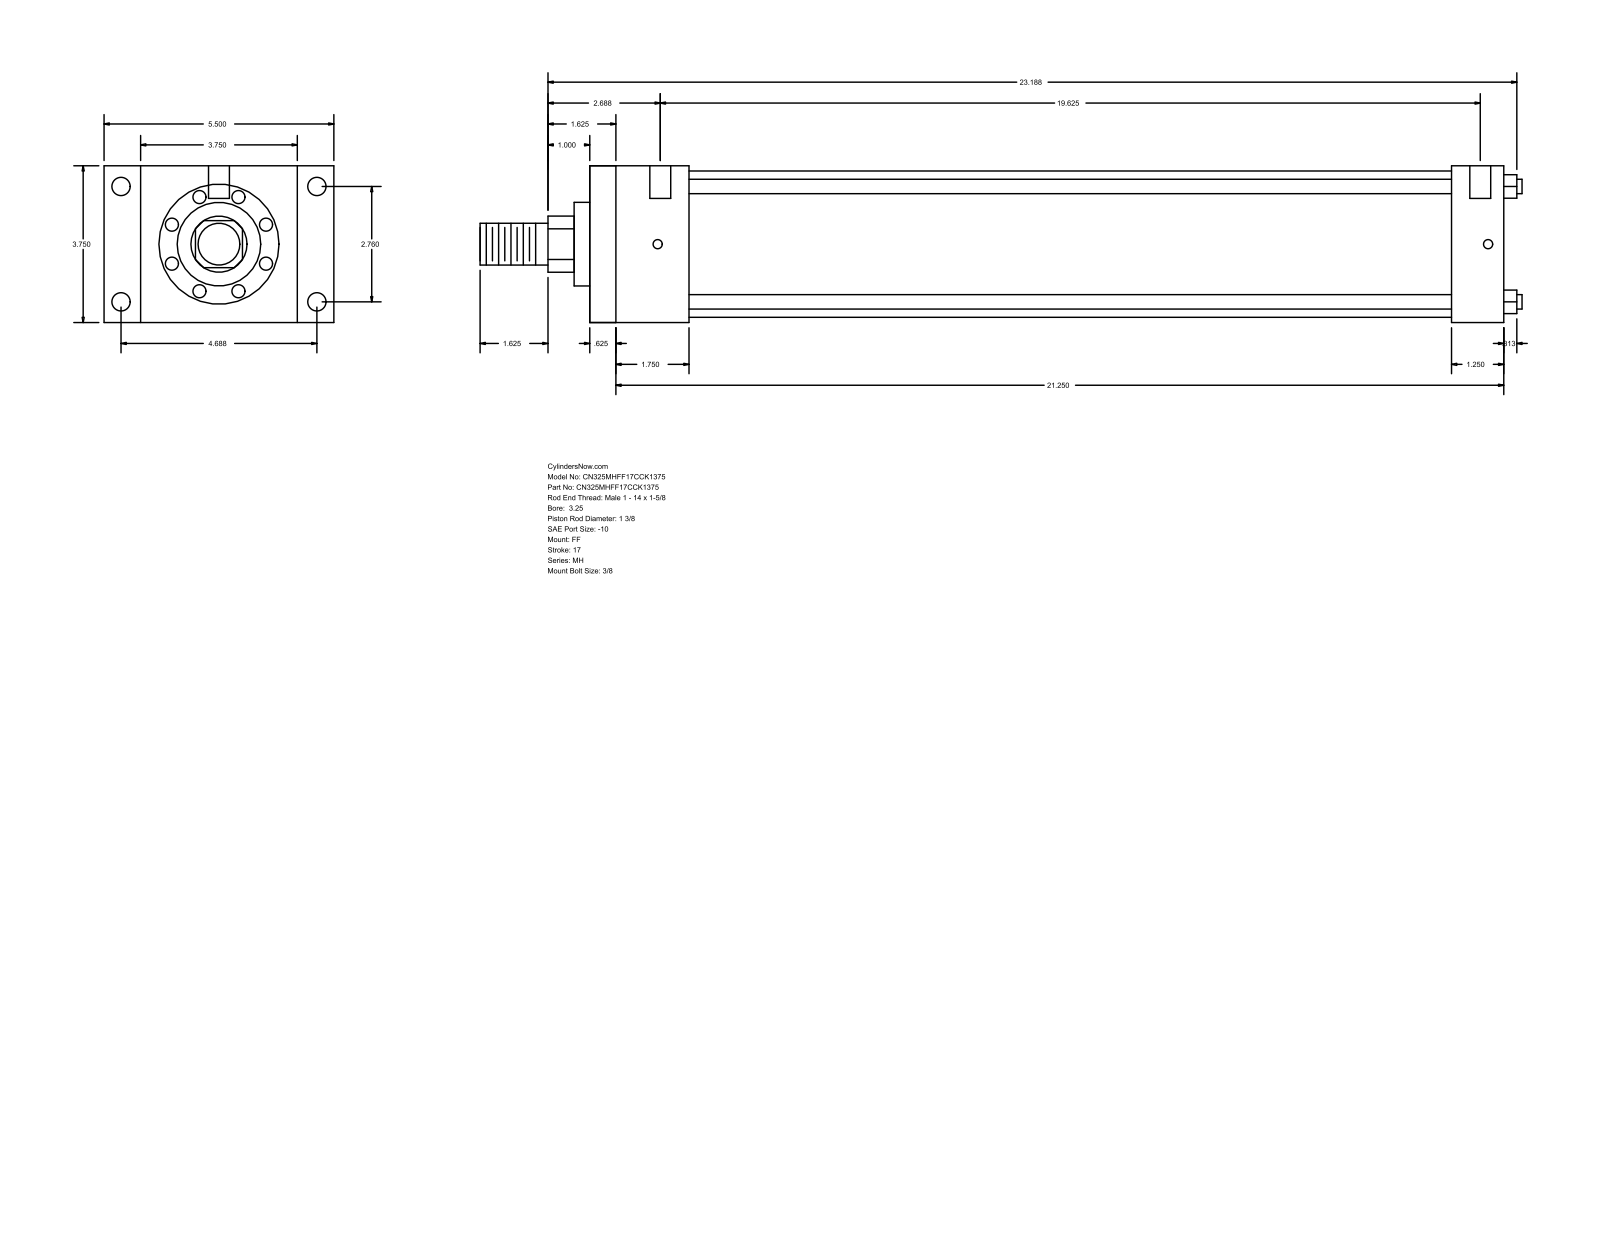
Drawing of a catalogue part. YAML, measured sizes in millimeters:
part_name: "MH_FF__0325_1.375"
step_written_by: "GSSL Pune (CONFIG_CONTROL_DESIGN)"
units: millimeters
bodies: {solids: 0, faces: 92, planar: 64, cylindrical: 28, other: 0}
overall_size: [633.41, 139.7, 95.25]
round_holes:
  - {diameter: 5.56, count: 4}
  - {diameter: 11.13, count: 4}
  - {diameter: 12.7, count: 2}
round_bosses_or_shafts:
  - {diameter: 8.76, count: 4}
  - {diameter: 88.9, count: 1}
  - {diameter: 50.8, count: 1}
  - {diameter: 34.92, count: 1}
  - {diameter: 25.4, count: 1}
partial_cylinders:
  - {radius: 17.06, count: 1}
face_to_face_distances: [95.24, 555.62, 15.87, 539.75, 22.23, 117.47, 523.87, 508, 31.75, 60.32]
hole_center_spacings: [70.1, 119.06, 138.16, 504.83, 1.59, 4.76, 498.48, 500.07]
